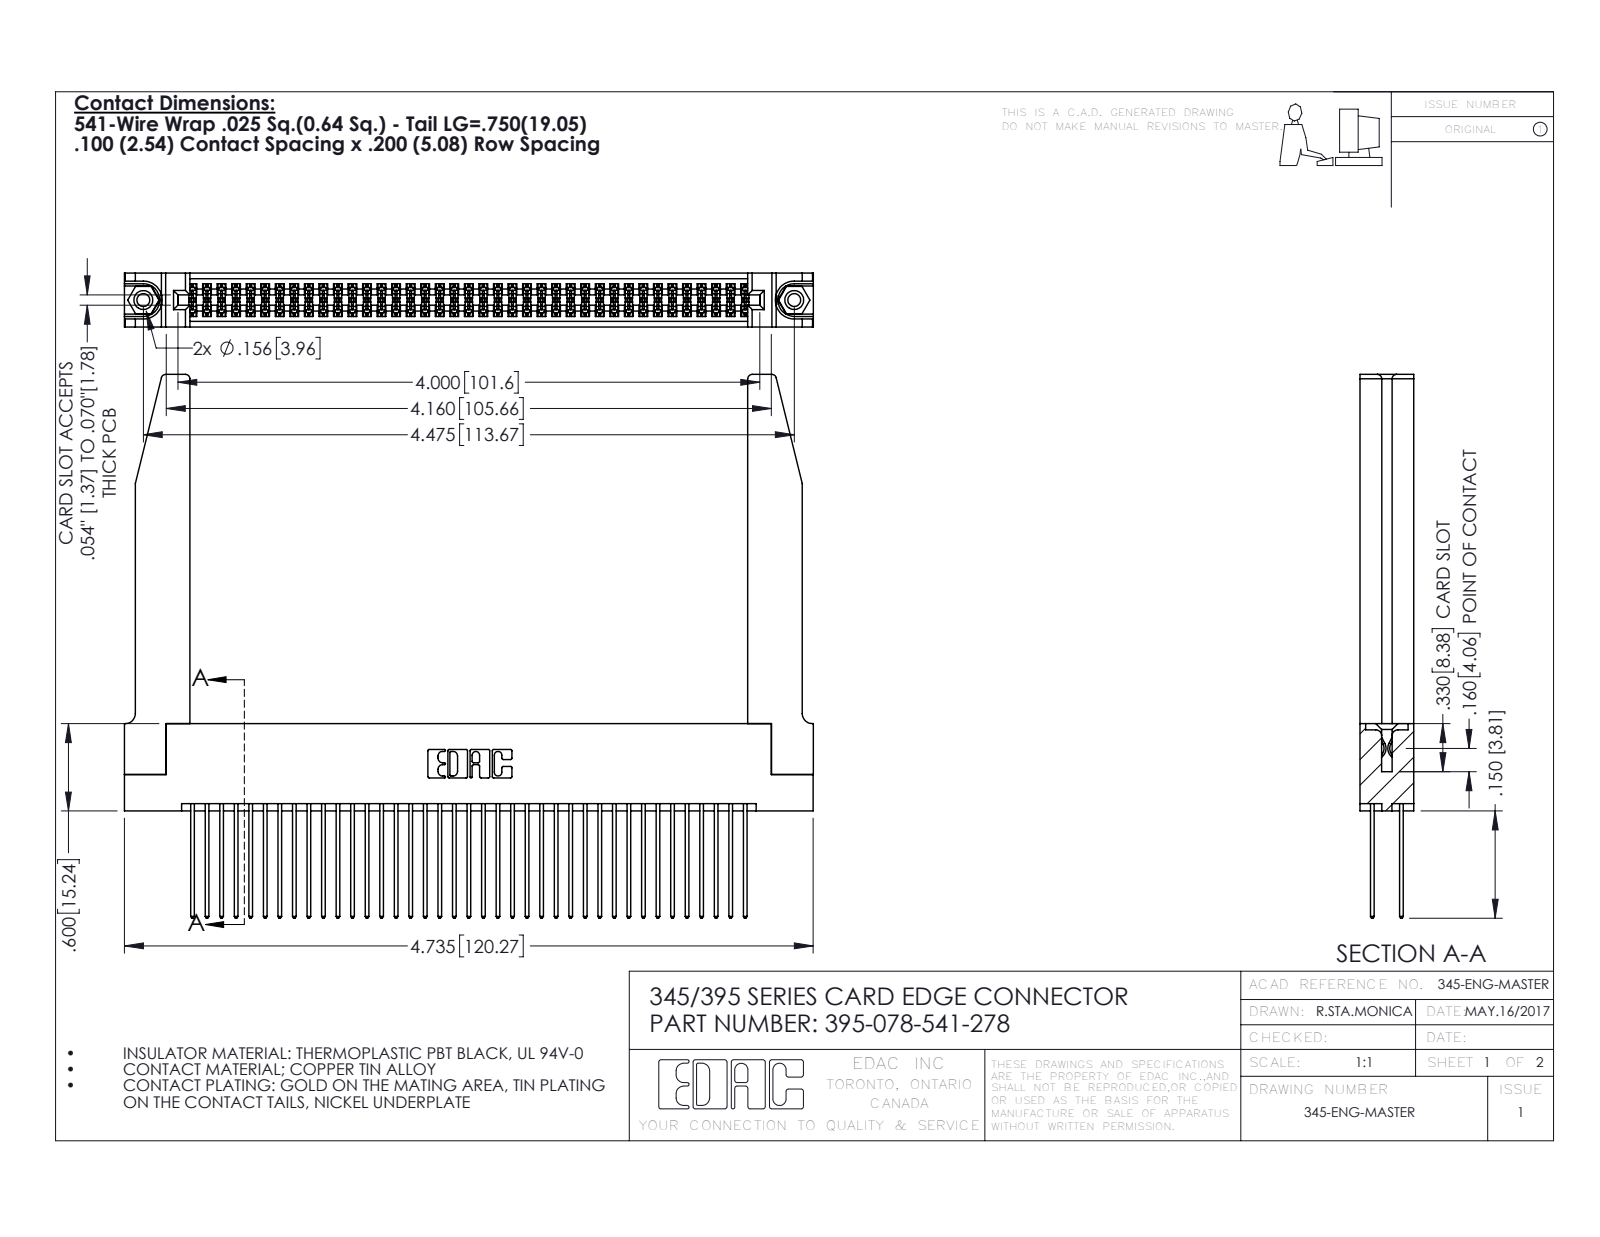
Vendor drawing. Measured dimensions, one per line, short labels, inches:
name: 395-078-541-278; 345-292-001_345-293-141; 345-220-078_345-220-078; 345 Part_Flush Mounting Lugs - 0.156 Dia-TH (+1 more)
written by: SolidWorks 2016 (CONFIG_CONTROL_DESIGN)
unit: in
bodies: 83 solids, 4260 faces (2796 planar, 1412 cylindrical, 52 other)
size: 4.736 × 3.737 × 0.37
volume: 1.213 in³; area: 41.51 in²
holes: 2× ⌀0.089, 2× ⌀0.125, 2× ⌀0.156, 1× ⌀0.064
bosses: 2× ⌀0.155
rounds: 117× R0.006, 78× R0.01, 22× R0.01, 8× R0.03, 6× R0.007, 6× R0.031, 3× R0.026, 2× R0.014
face distances: 0.072, 0.298, 0.37, 0.2, 0.098, 0.272, 0.025, 0.225, 0.175, 0.148
hole spacings: 0.27, 4.239, 4.475
